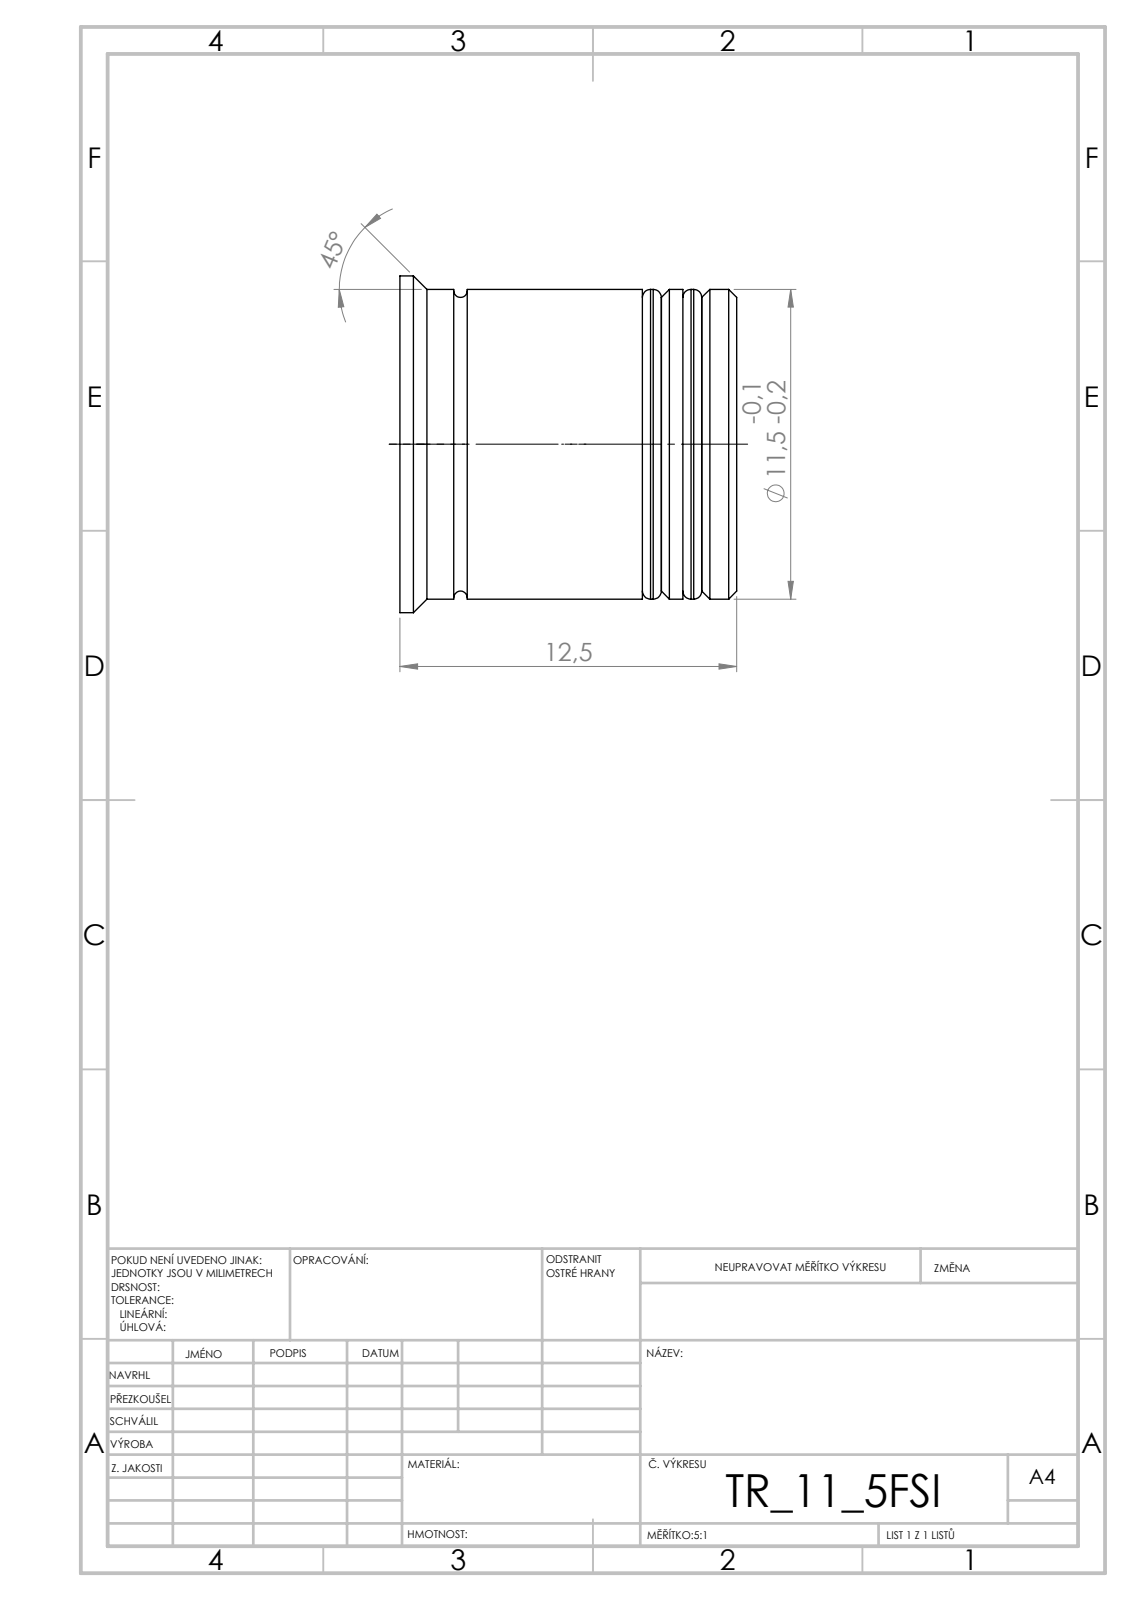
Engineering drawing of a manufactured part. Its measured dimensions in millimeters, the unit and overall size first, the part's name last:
Units: millimetres
Overall size (bounding box): 12.5 × 12.5 × 12.5
Round bosses / shafts (diameter × count): ⌀12.5 ×1, ⌀11.5 ×1, ⌀10.9 ×1, ⌀8.5 ×1
Main face-to-face distances: 1.5, 0.7, 2, 2.2, 0.8, 1.3, 2.8, 3.5, 9.5, 1
Volume: 1 361 mm³ · Surface area: 1 251 mm²
Bodies: 3 solids, 74 faces (29 planar, 25 cylindrical, 20 other)
STEP written by: SolidWorks 2019 (CONFIG_CONTROL_DESIGN)
